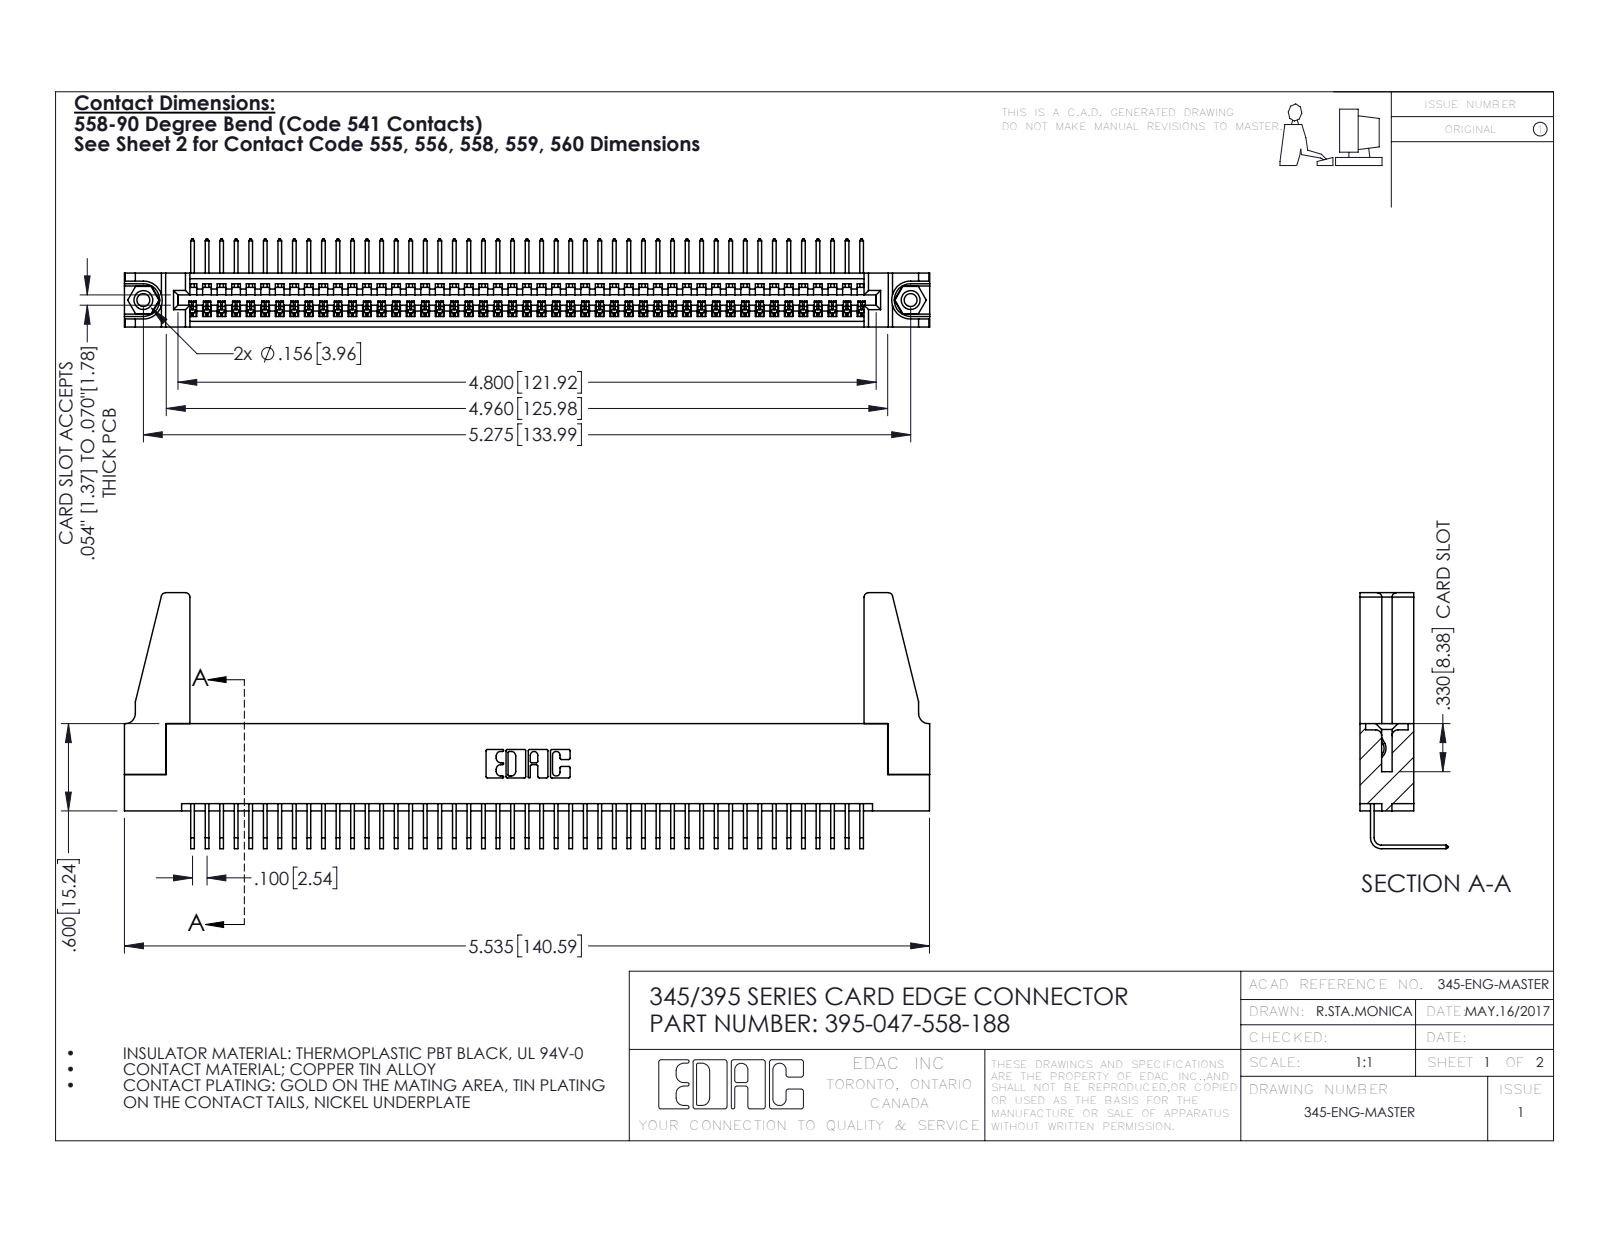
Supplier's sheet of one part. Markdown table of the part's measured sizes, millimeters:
| quantity | value |
| --- | --- |
| part name | 345-250-001_345-250-001-102; 345-292-001_558 Tail - 2; 345-220-078_345-220-088; 395-047-558-188 (+1 more) |
| STEP written by | SolidWorks 2016 (CONFIG_CONTROL_DESIGN) |
| units | millimeters |
| bodies | 52 solids, 3070 faces (2126 planar, 928 cylindrical, 16 other) |
| overall size | 140.6 × 44.7 × 15.4 |
| volume | 16 810 mm³ |
| surface area | 22 130 mm² |
| round holes (diameter × count) | 2.3 × 2, 3.2 × 2, 4 × 2, 1.6 × 1 |
| round bosses / shafts (diameter × count) | 3.9 × 2 |
| partial cylindrical surfaces (radius × count) | 0.2 × 94, 0.3 × 22, 0.8 × 8, 0.2 × 6, 0.8 × 6, 0.7 × 3, 0.8 × 2, 1 × 2 |
| main face-to-face distances | 1.8, 7.6, 9.4, 5.1, 2.5, 6.9, 0.6, 5.7, 3.8, 1.8 |
| hole center spacings | 6.9, 128, 134 |
